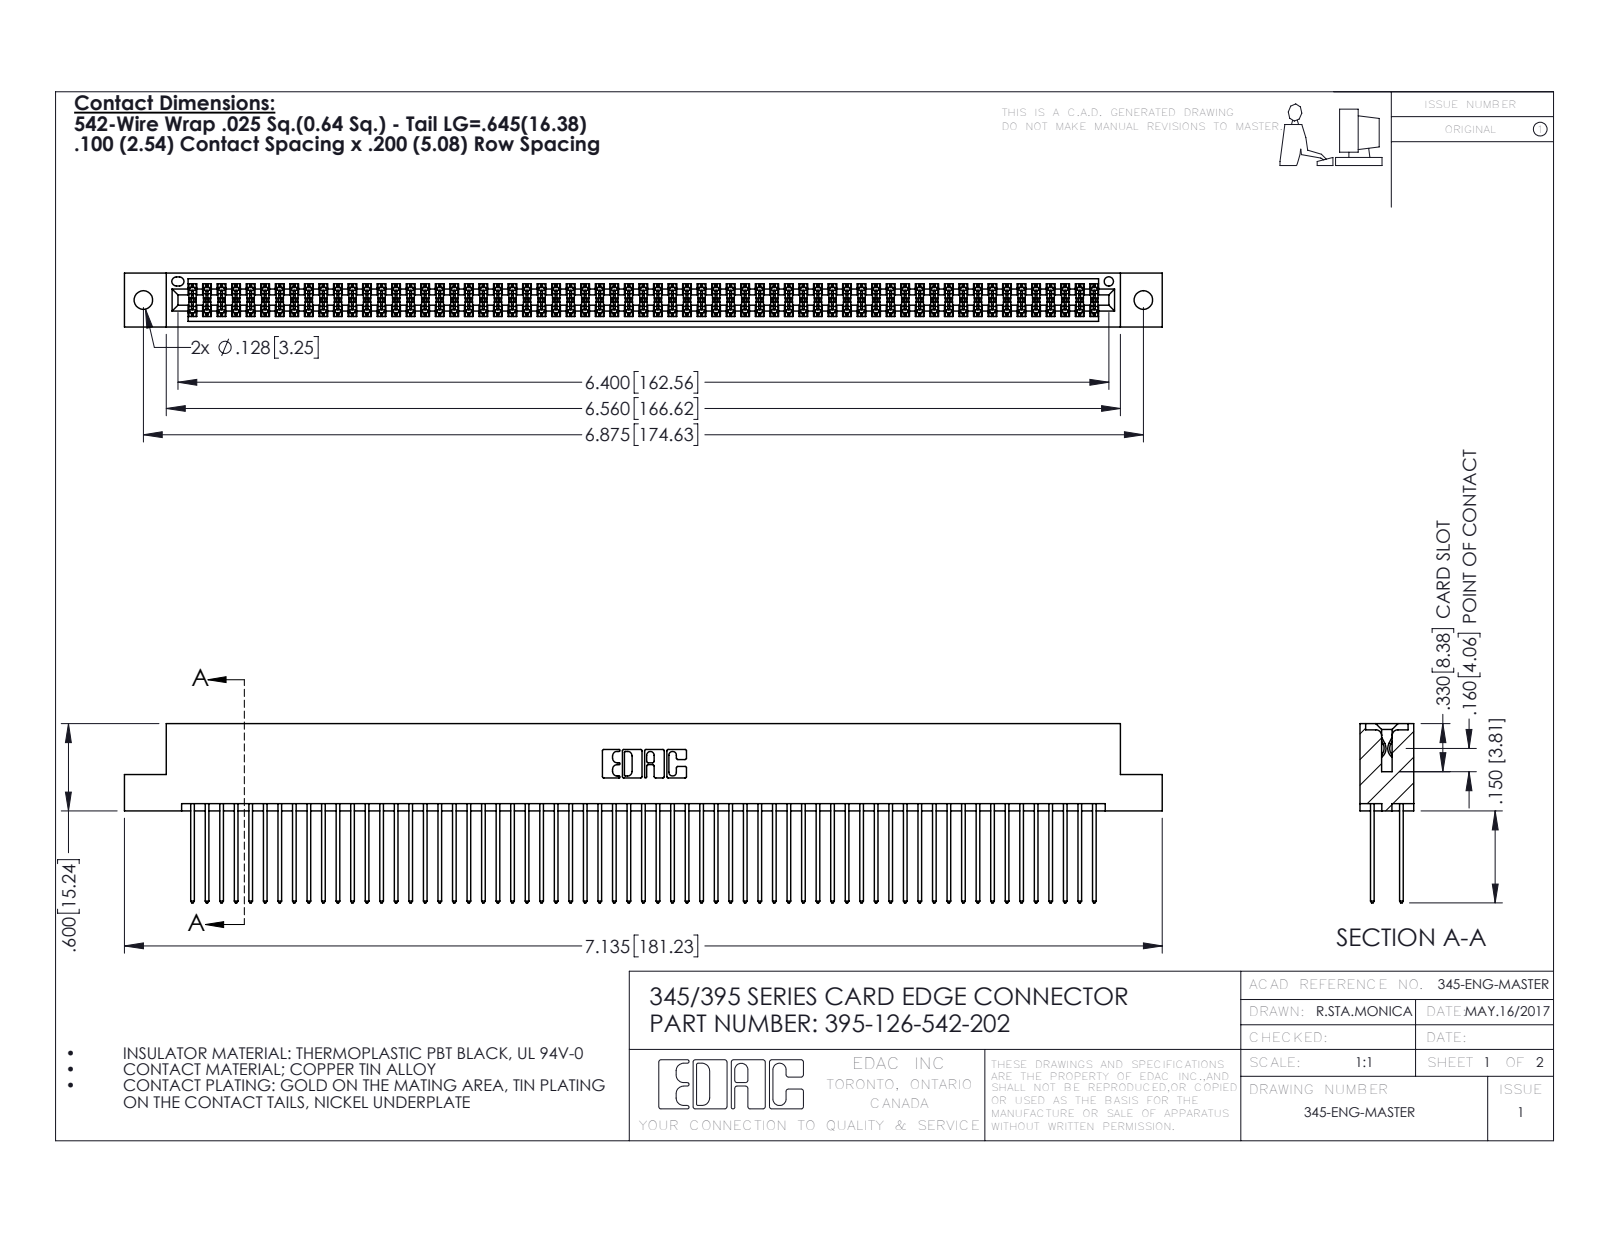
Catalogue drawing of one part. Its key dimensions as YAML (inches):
part_name: "345-292-001_345-293-142; 395-126-542-202; 345 Part_Flush Mounting Lugs - 0.128 Dia"
step_written_by: "SolidWorks 2016 (CONFIG_CONTROL_DESIGN)"
units: inches
bodies: {solids: 127, faces: 6426, planar: 4238, cylindrical: 2188, other: 0}
overall_size: [7.135, 1.232, 0.37]
volume: 1.12
surface_area: 46.51
round_holes:
  - {diameter: 0.128, count: 2}
  - {diameter: 0.064, count: 1}
partial_cylinders:
  - {radius: 0.006, count: 189}
  - {radius: 0.01, count: 126}
  - {radius: 0.01, count: 22}
  - {radius: 0.007, count: 6}
  - {radius: 0.031, count: 6}
  - {radius: 0.026, count: 3}
  - {radius: 0.014, count: 2}
  - {radius: 0.019, count: 2}
face_to_face_distances: [0.298, 0.072, 0.2, 0.098, 0.272, 0.025, 0.225, 0.37, 0.175, 0.149]
hole_center_spacings: [0.27, 6.639, 6.875]
